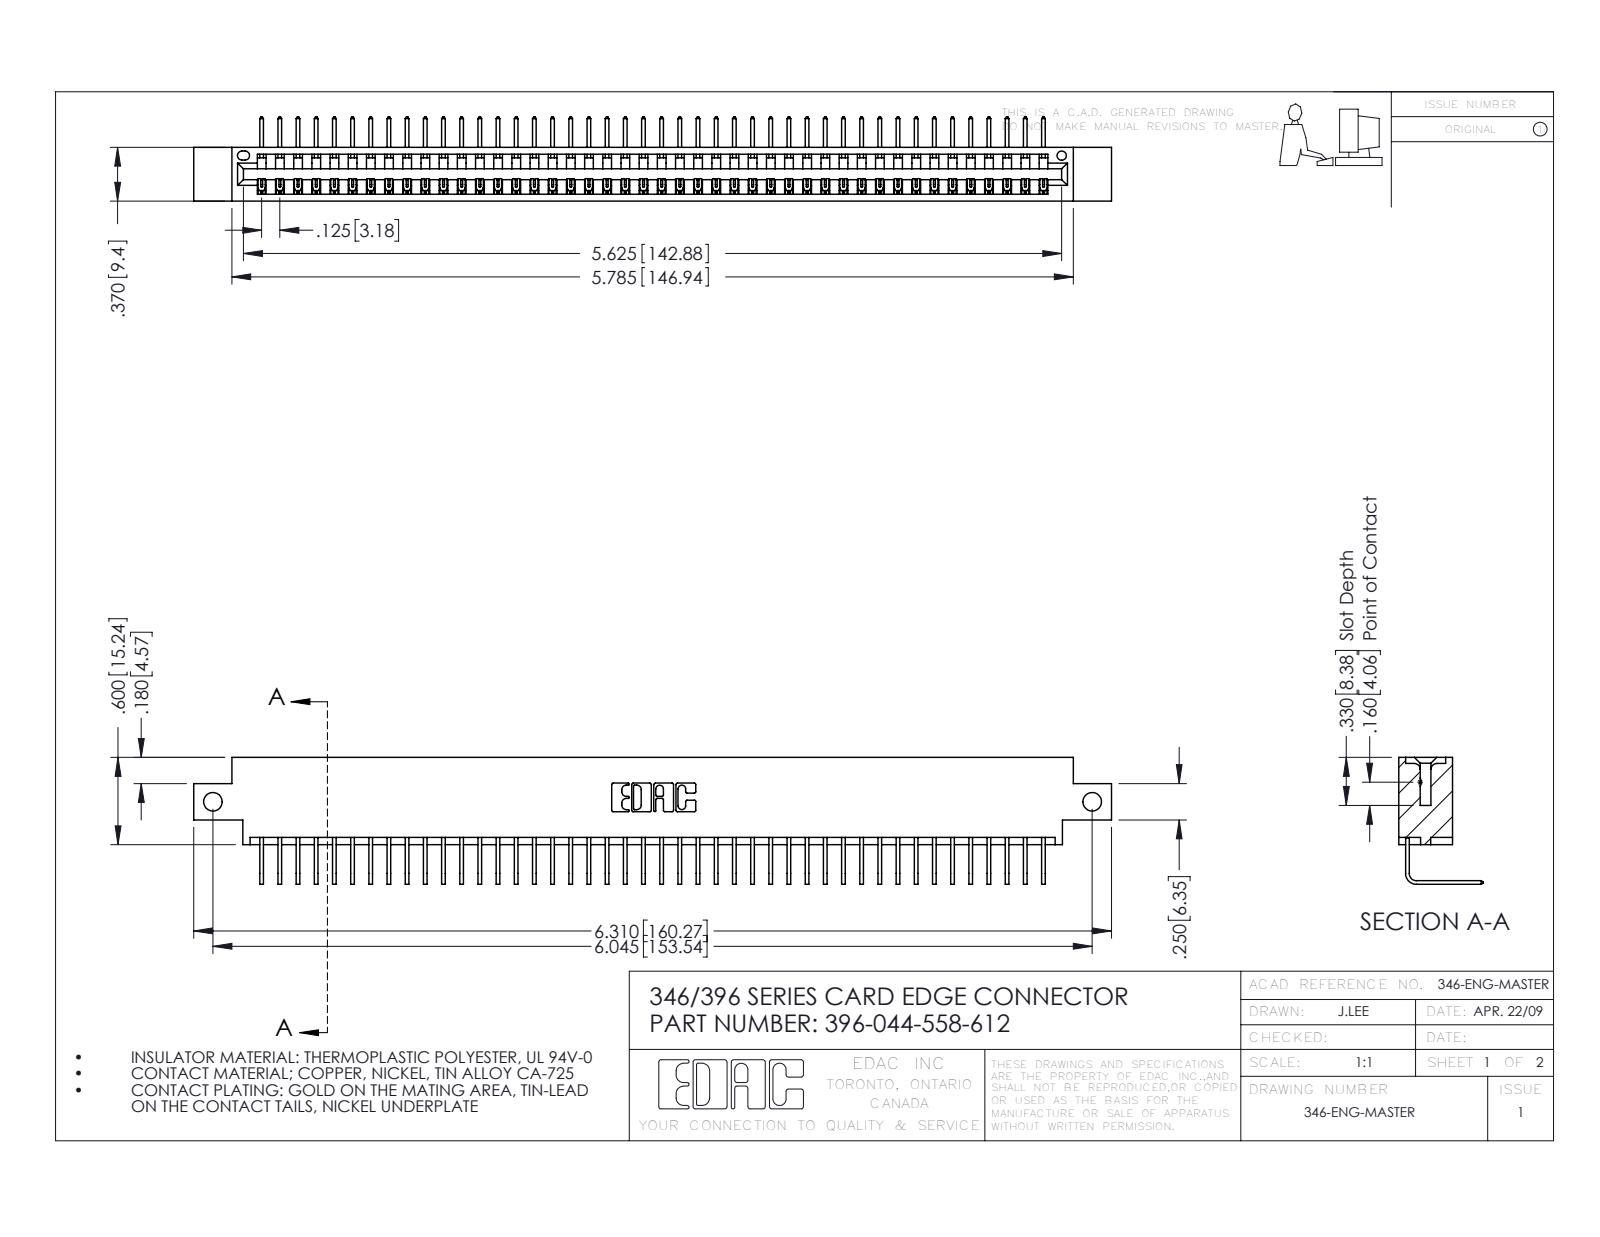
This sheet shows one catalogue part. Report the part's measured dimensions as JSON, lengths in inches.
{"part_name": "346 Part_0.170 Offset - Side Mount; 345-292-001_558 Tail - 2; 396-044-558-612", "step_written_by": "SolidWorks 2016 (CONFIG_CONTROL_DESIGN)", "units": "inches", "bodies": {"solids": 45, "faces": 2766, "planar": 1928, "cylindrical": 838, "other": 0}, "overall_size": [6.31, 0.873, 0.58], "volume_in3": 0.931, "surface_area_in2": 30.98, "round_holes": [[0.128, 2], [0.064, 1]], "partial_cylinders_radius": [[0.006, 88], [0.01, 22], [0.007, 6], [0.031, 6], [0.026, 3], [0.031, 2], [0.04, 2], [0.014, 1]], "face_to_face_distances": [0.322, 0.048, 0.37, 0.25, 0.298, 0.025, 0.072, 0.148, 0.222, 0.1], "hole_center_spacings": [6.045]}
